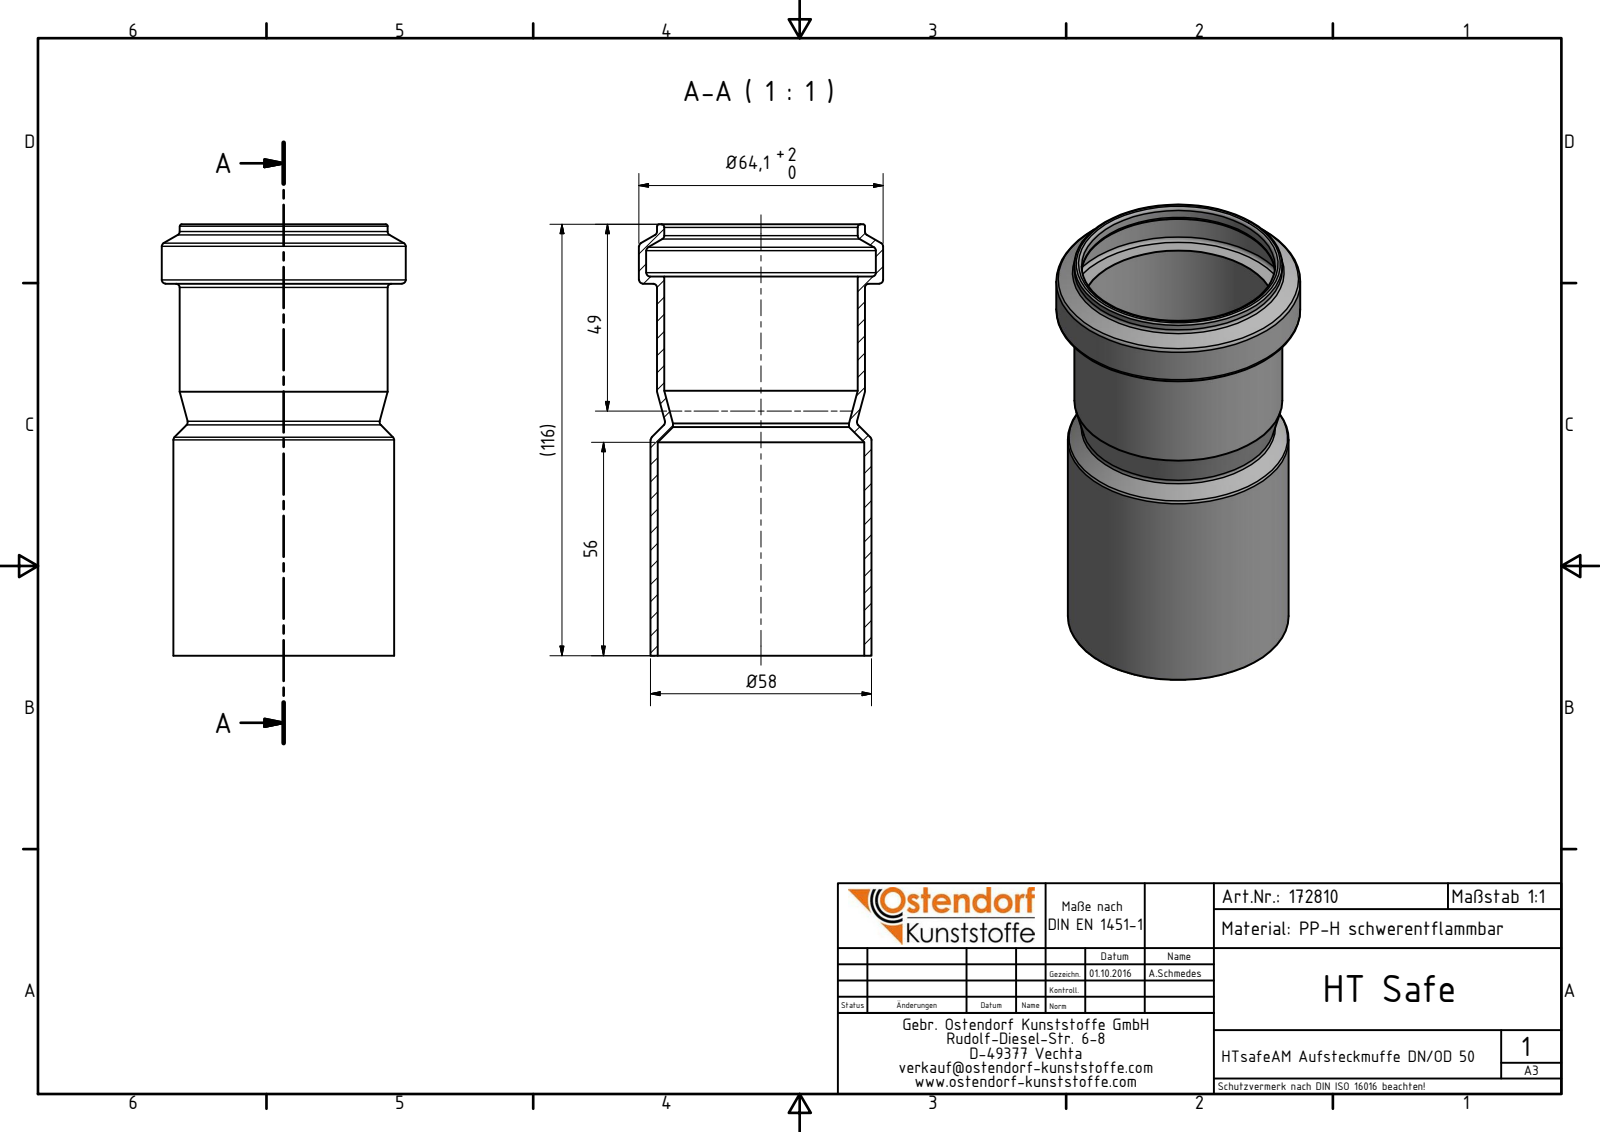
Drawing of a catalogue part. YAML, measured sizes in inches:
part_name: "172810 HTsafeAM DN_OD 50"
step_written_by: "Autodesk Inventor 2016 (AUTOMOTIVE_DESIGN)"
units: inches
bodies: {solids: 1, faces: 30, planar: 4, cylindrical: 9, other: 17}
overall_size: [4.457, 2.524, 2.524]
volume: 2.473
surface_area: 66.19
round_holes:
  - {diameter: 1.819, count: 1}
  - {diameter: 2, count: 1}
  - {diameter: 2.134, count: 1}
  - {diameter: 2.374, count: 1}
round_bosses_or_shafts:
  - {diameter: 2.524, count: 1}
  - {diameter: 2.283, count: 1}
  - {diameter: 2.15, count: 1}
face_to_face_distances: [0.075, 3.843, 3.917, 4.457, 0.614, 0.539]
